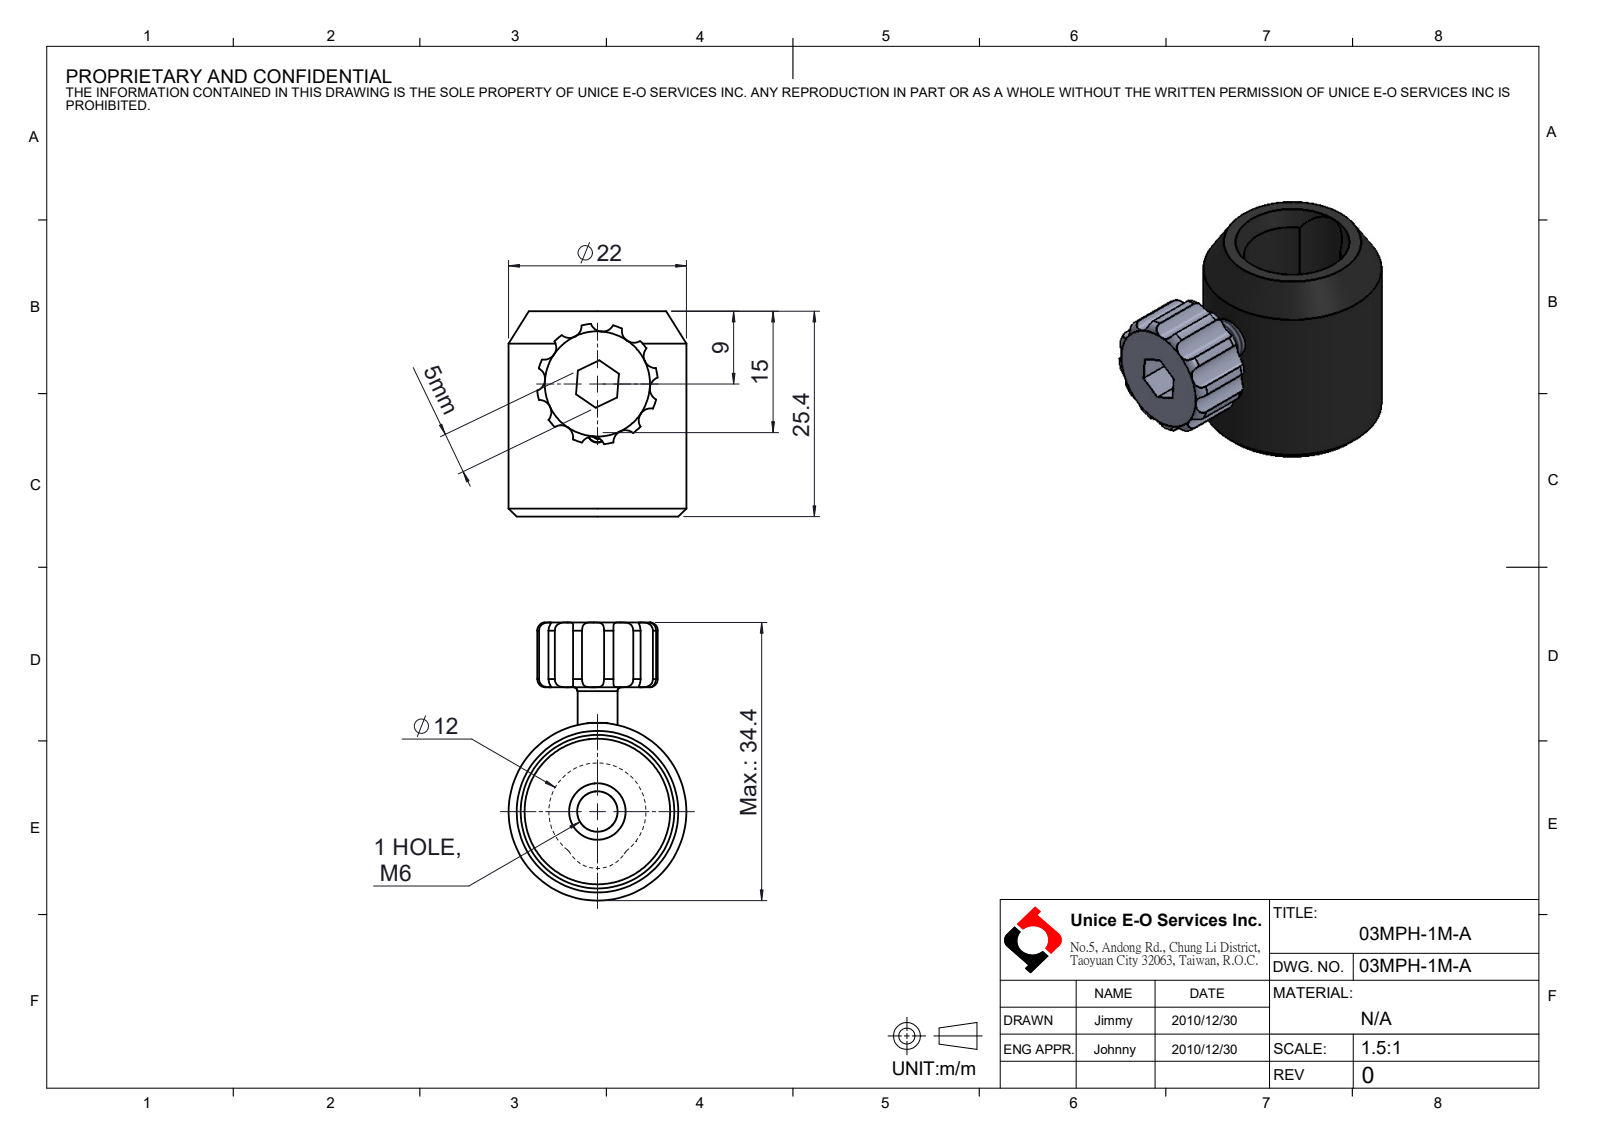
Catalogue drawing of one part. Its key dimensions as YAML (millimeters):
part_name: "03MPH-1M-A"
step_written_by: "SolidWorks 2016 (CONFIG_CONTROL_DESIGN)"
units: millimeters
bodies: {solids: 6, faces: 126, planar: 25, cylindrical: 49, other: 52}
overall_size: [34.4, 25.4, 22]
volume: 8217
surface_area: 5399
round_holes:
  - {diameter: 5, count: 2}
  - {diameter: 2.3, count: 1}
  - {diameter: 2.5, count: 1}
  - {diameter: 12.05, count: 1}
  - {diameter: 19, count: 1}
round_bosses_or_shafts:
  - {diameter: 22, count: 1}
  - {diameter: 4.94, count: 1}
  - {diameter: 3, count: 1}
partial_cylinders:
  - {radius: 1.5, count: 12}
  - {radius: 4.01, count: 1}
  - {radius: 7.5, count: 1}
face_to_face_distances: [8, 25.4, 17.4, 4.2, 3.8, 5.1, 5.11, 1.5, 7.4, 11.6]
hole_center_spacings: [6]
